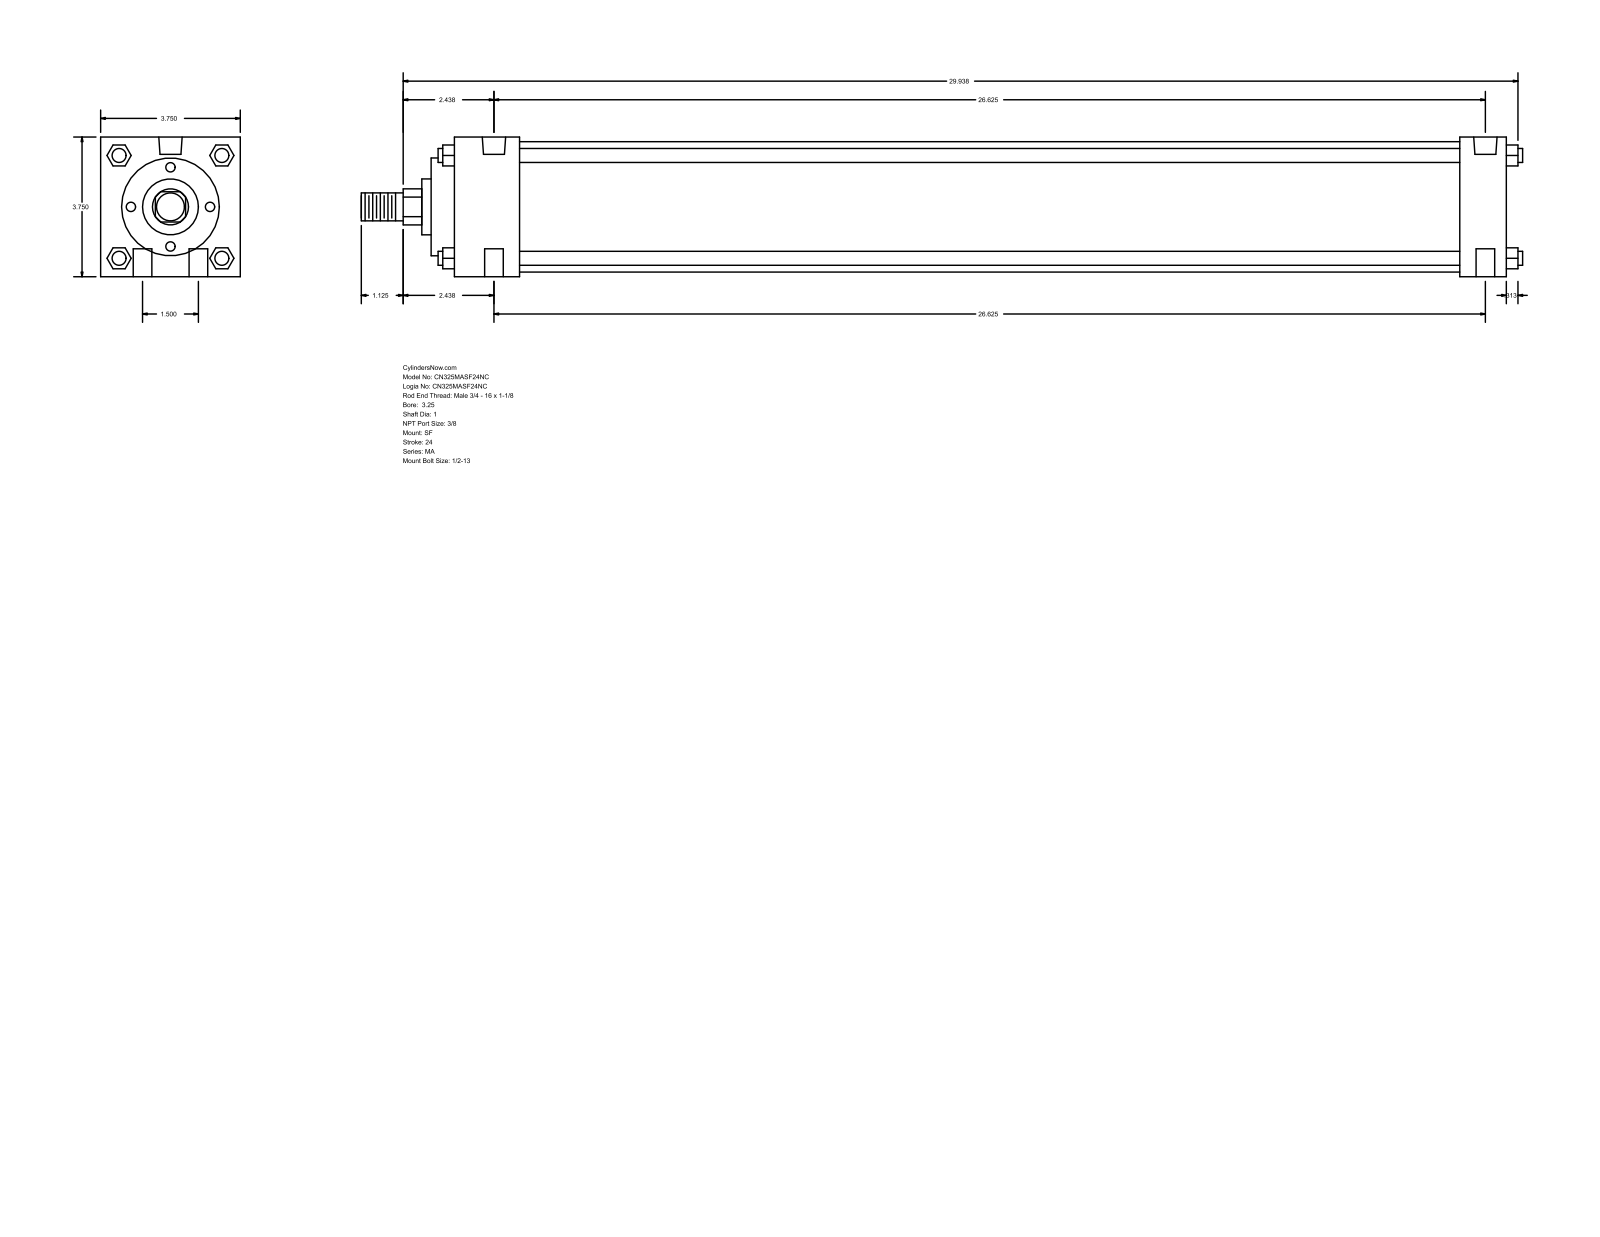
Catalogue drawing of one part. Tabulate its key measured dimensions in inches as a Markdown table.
| quantity | value |
| --- | --- |
| part name | MA_SF__0325_1 |
| STEP written by | GSSL Pune (CONFIG_CONTROL_DESIGN) |
| units | inches |
| bodies | 0 solids, 126 faces (95 planar, 31 cylindrical, 0 other) |
| overall size | 31.187 × 3.75 × 3.75 |
| round holes (diameter × count) | 0.5 × 4, 0.437 × 2, 0.627 × 2 |
| round bosses / shafts (diameter × count) | 0.375 × 4, 3.5 × 1, 2.625 × 1, 1.5 × 1, 1 × 1, 0.75 × 1 |
| partial cylindrical surfaces (radius × count) | 0.484 × 1 |
| main face-to-face distances | 3.75, 28.25, 27, 1.25, 1.75, 25.25, 26.5, 0.625, 2.375, 27.625 |
| hole center spacings | 0.75, 26.636, 26.625, 1.5, 26.667, 26.25 |
